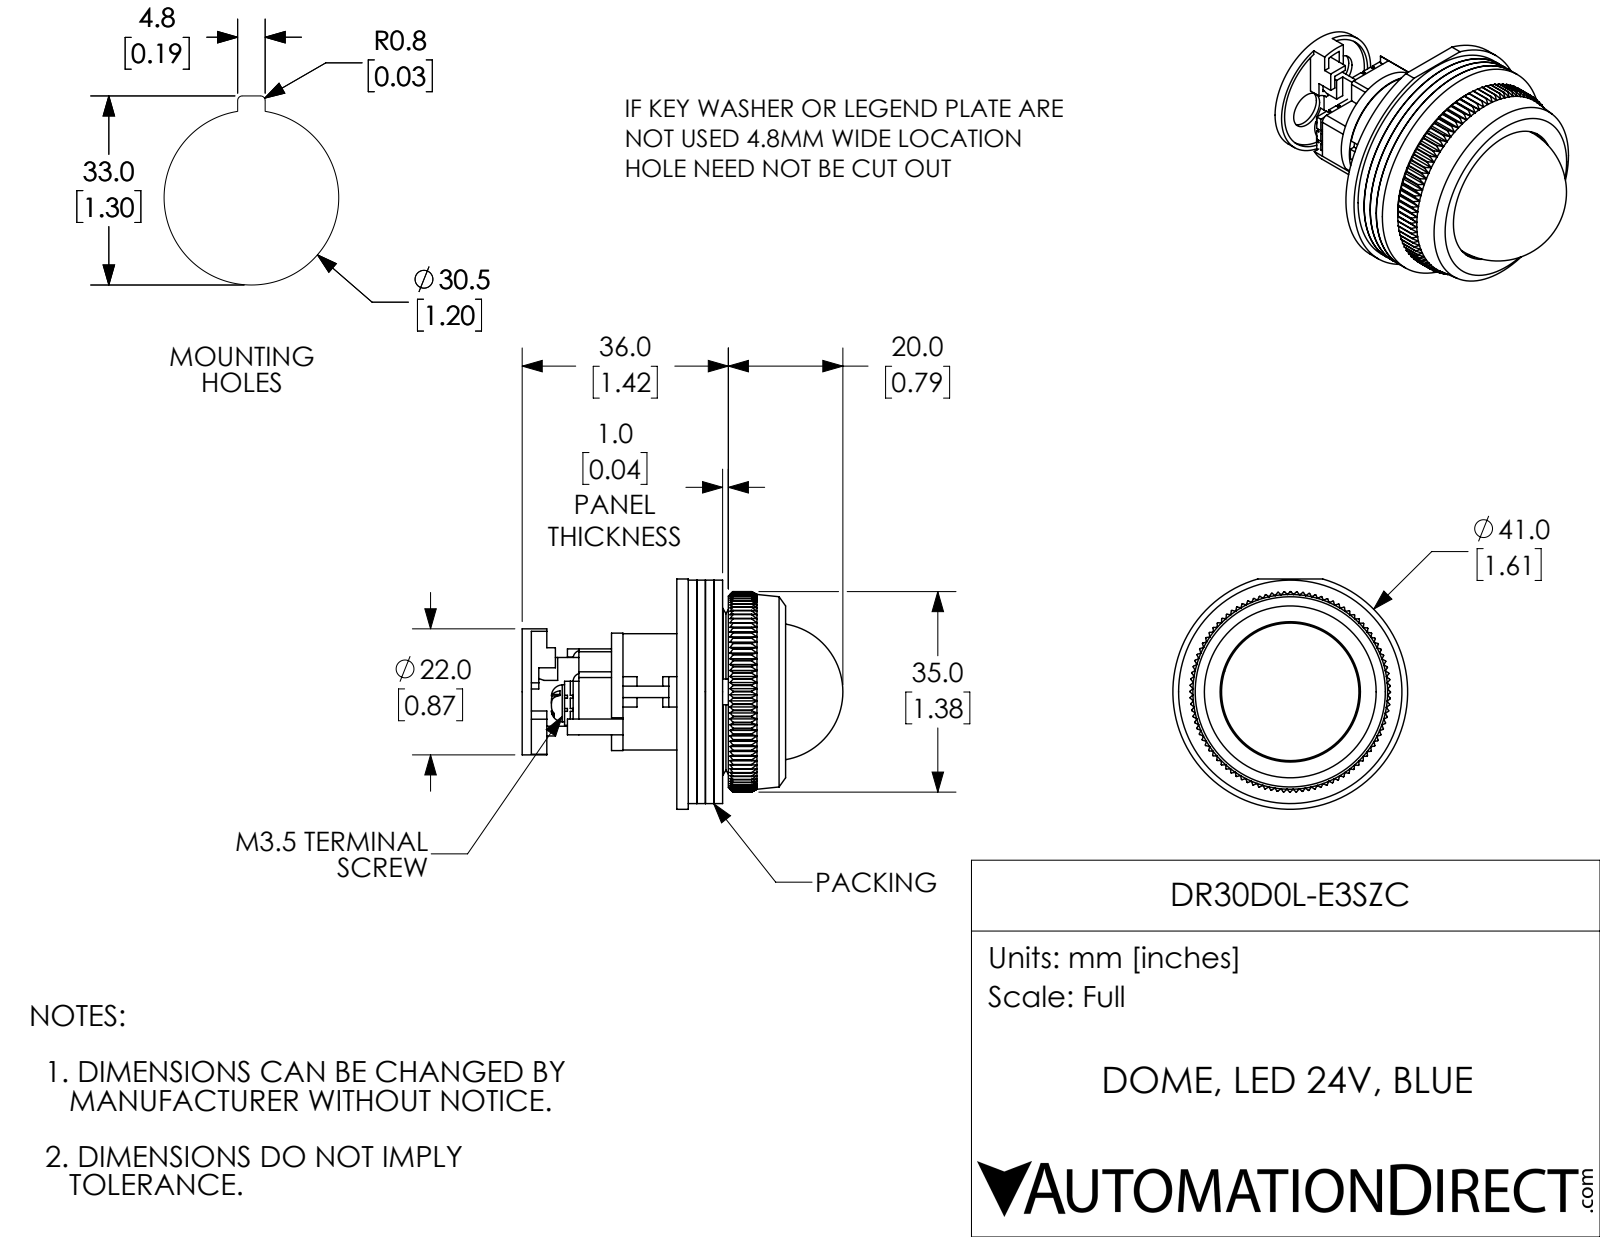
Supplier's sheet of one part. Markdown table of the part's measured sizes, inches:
| quantity | value |
| --- | --- |
| part name | DR30D0L-E3SZC |
| STEP written by | SolidWorks 2017 (AUTOMOTIVE_DESIGN) |
| units | inches |
| bodies | 16 solids, 1350 faces (770 planar, 336 cylindrical, 244 other) |
| overall size | 2.203 × 1.614 × 1.583 |
| volume | 1.045 in³ |
| surface area | 37.94 in² |
| round holes (diameter × count) | 0.118 × 2, 0.138 × 2, 0.252 × 2, 0.362 × 1, 0.461 × 1, 0.543 × 1, 0.563 × 1, 0.583 × 1, 0.63 × 1, 0.709 × 1, 0.72 × 1, 0.787 × 1 |
| round bosses / shafts (diameter × count) | 0.063 × 2, 1.614 × 1, 1.535 × 1, 1.16 × 1, 0.945 × 1, 0.858 × 1, 0.819 × 1, 0.799 × 1 |
| partial cylindrical surfaces (radius × count) | 0.059 × 8, 0.01 × 5, 0.022 × 5, 0.016 × 4, 0.055 × 4, 0.02 × 2, 0.039 × 2, 0.146 × 2 |
| main face-to-face distances | 0.059, 0.118, 0.177, 0.039, 0.197, 0.079, 0.315, 0.256, 0.098, 0.236 |
| hole center spacings | 0.176, 0.185, 0.361, 0.352, 0.37 |
